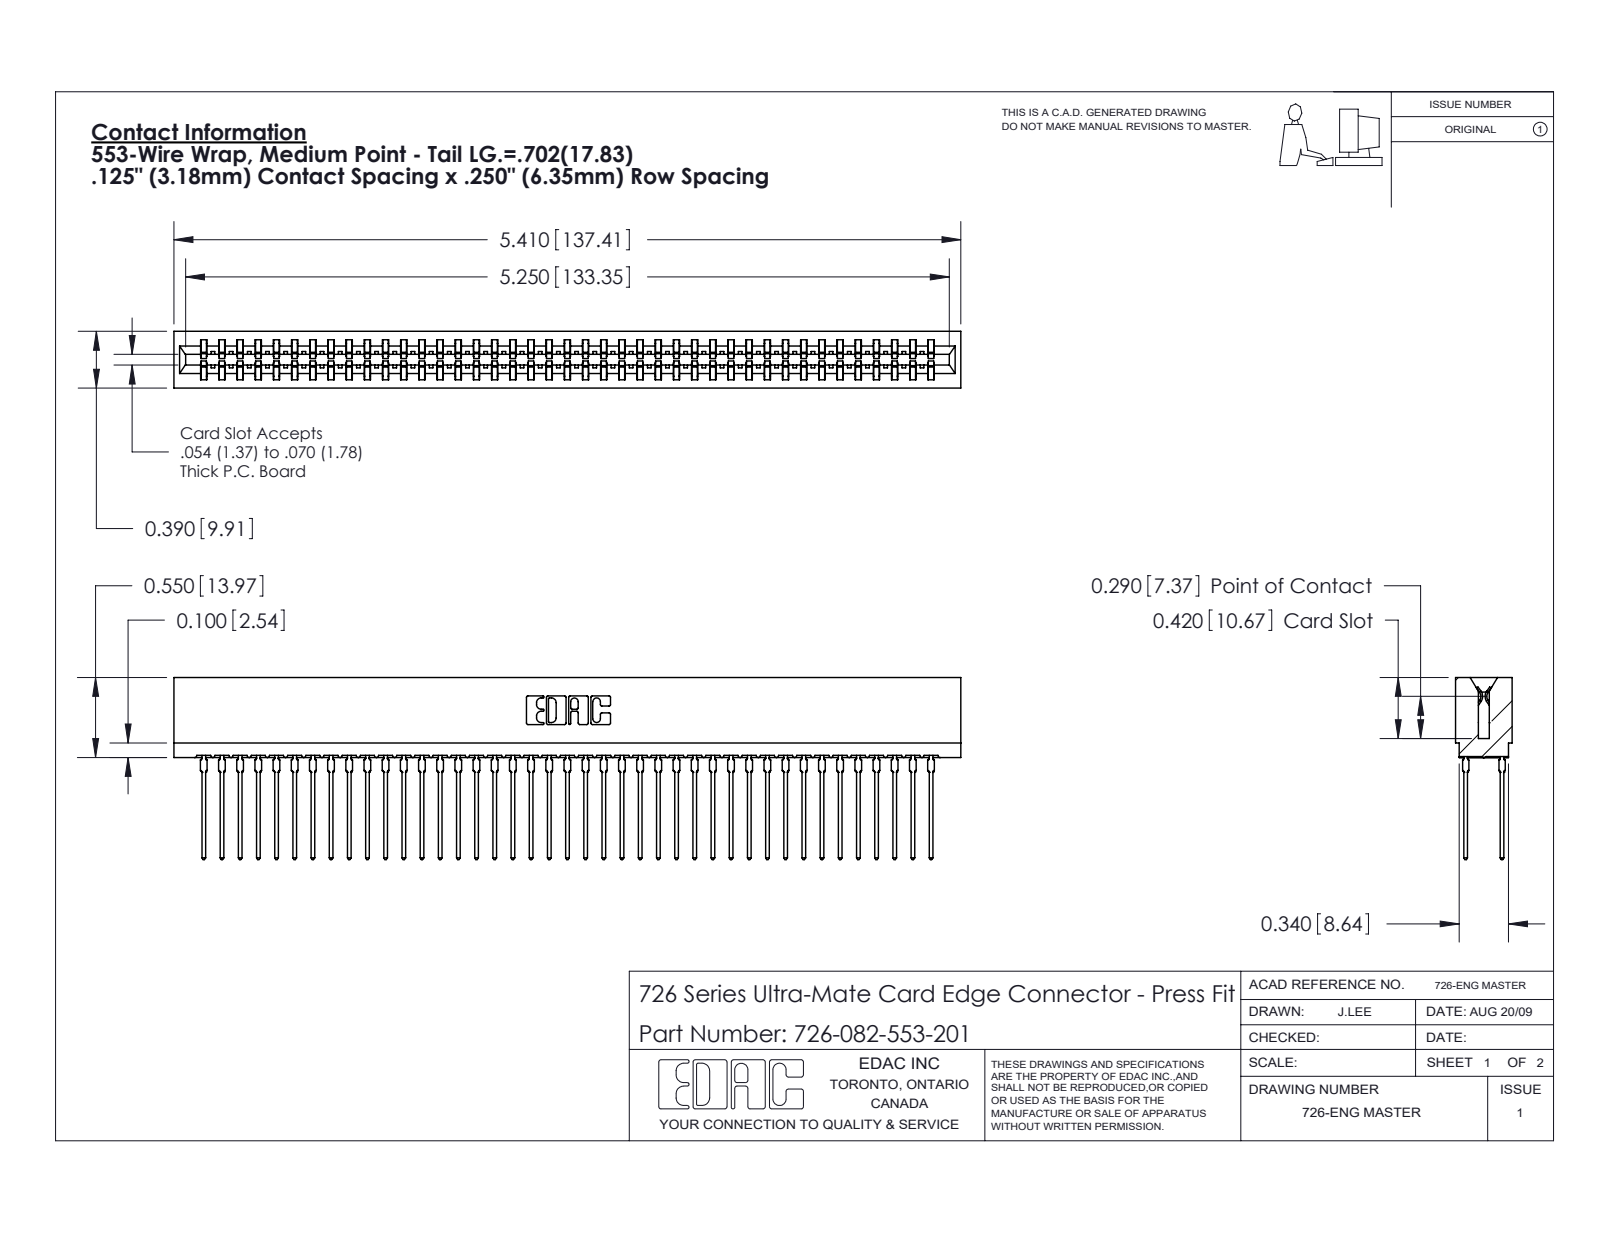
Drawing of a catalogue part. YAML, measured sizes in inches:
part_name: "726 Part_.515 Slot Depth - 01; 726-082-553-201; 746-292-001_553"
step_written_by: "SolidWorks 2020 (CONFIG_CONTROL_DESIGN)"
units: inches
bodies: {solids: 83, faces: 7436, planar: 3827, cylindrical: 1477, other: 2132}
overall_size: [5.41, 1.251, 0.39]
volume: 0.795
surface_area: 36.17
partial_cylinders:
  - {radius: 0.021, count: 164}
  - {radius: 0.015, count: 42}
  - {radius: 0.01, count: 22}
  - {radius: 0.005, count: 8}
  - {radius: 0.011, count: 8}
  - {radius: 0.007, count: 6}
  - {radius: 0.031, count: 6}
  - {radius: 0.026, count: 3}
face_to_face_distances: [0.057, 0.333, 0.025, 0.307, 0.25, 0.39, 0.083, 0.275, 0.225, 0.365]
